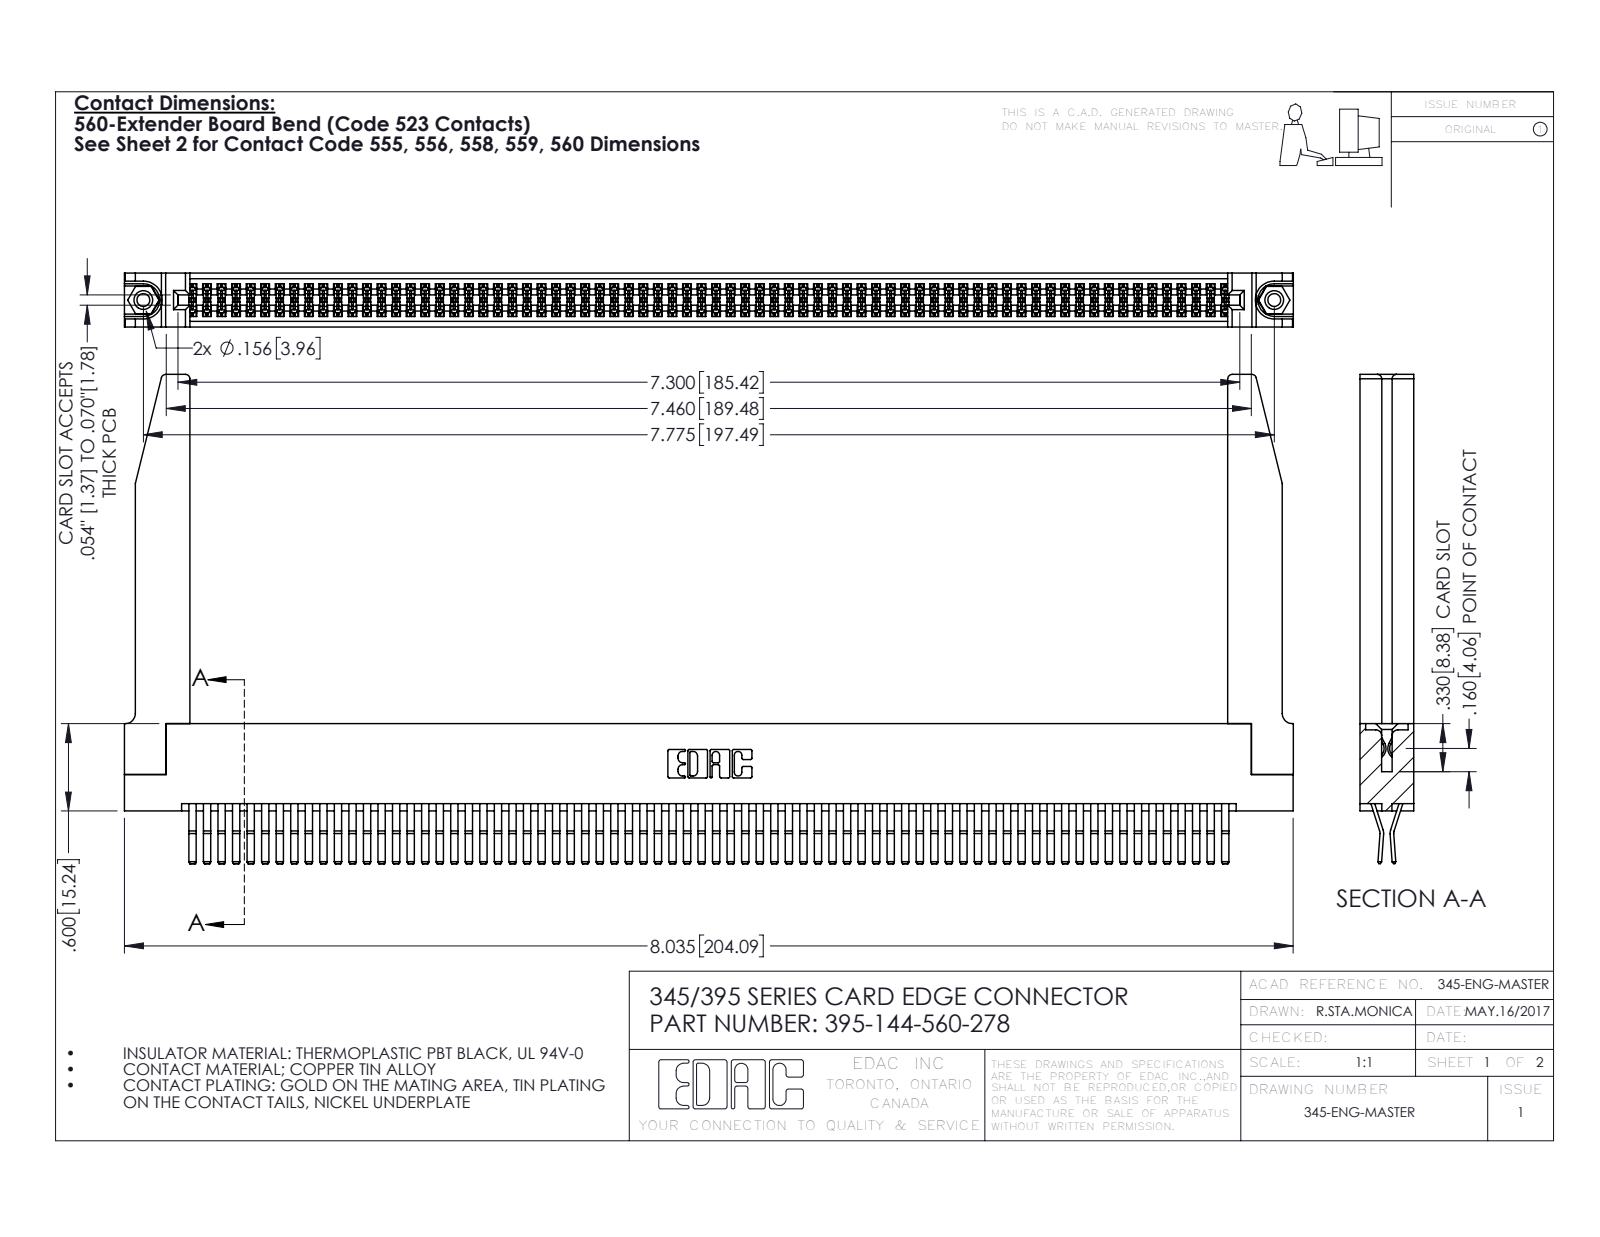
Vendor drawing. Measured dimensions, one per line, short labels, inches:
name: 345-292-001_560 Tail; 345-220-078_345-220-078; 395-144-560-278; 345-250-001_345-250-001-102 (+1 more)
written by: SolidWorks 2016 (CONFIG_CONTROL_DESIGN)
unit: in
bodies: 149 solids, 7848 faces (4974 planar, 2822 cylindrical, 52 other)
size: 8.036 × 3.362 × 0.37
volume: 1.759 in³; area: 63.49 in²
holes: 2× ⌀0.089, 2× ⌀0.125, 2× ⌀0.156, 1× ⌀0.064
bosses: 2× ⌀0.155
rounds: 216× R0.006, 22× R0.01, 8× R0.03, 6× R0.007, 6× R0.031, 3× R0.026, 2× R0.01, 2× R0.014
face distances: 0.072, 0.025, 0.298, 0.37, 0.2, 0.098, 0.272, 0.225, 0.175, 0.149
hole spacings: 0.27, 7.539, 7.775
